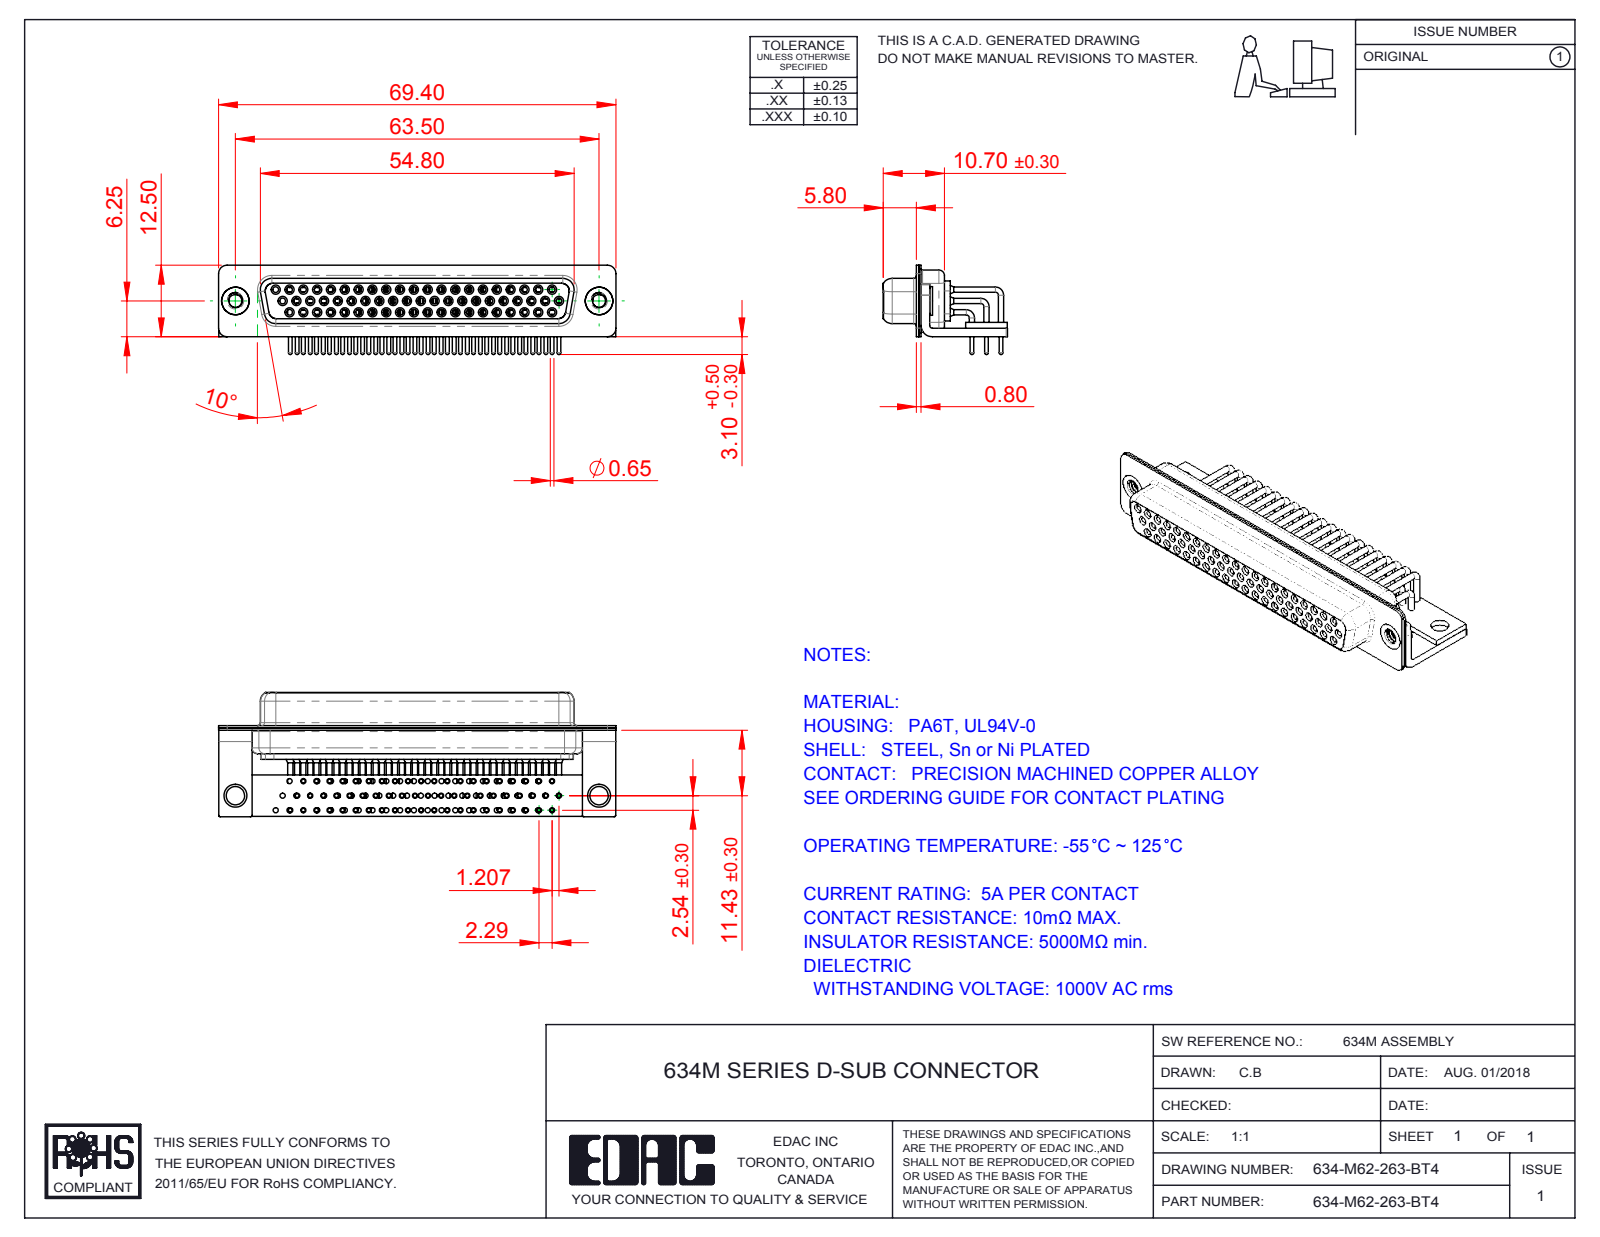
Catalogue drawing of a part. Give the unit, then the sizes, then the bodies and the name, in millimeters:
Units: millimetres
Overall size (bounding box): 69.4 × 21.7 × 15.6
Round holes (diameter × count): ⌀0.9 ×62, ⌀1 ×62, ⌀1.1 ×62, ⌀1.7 ×62, ⌀1.8 ×62, ⌀2 ×62, ⌀2.26 ×2, ⌀3.2 ×2, ⌀4 ×2, ⌀4.8 ×2
Round bosses / shafts (diameter × count): ⌀0.9 ×118, ⌀1.6 ×62, ⌀1.5 ×62, ⌀0.65 ×62, ⌀2 ×56, ⌀5 ×2, ⌀4.9 ×2
Partial cylindrical surfaces — rounded edges, fillets, slot ends (radius × count): R0.25 ×16, R1.5 ×16, R2 ×13, R1.35 ×8, R1.6 ×8, R0.5 ×5, R0.6 ×4, R0.65 ×4
Main face-to-face distances: 0.4, 2.3, 1.9, 1, 1.45, 8.95, 8.5, 0.85, 0.8, 9.35
Hole centre spacings: 7.24, 2.41, 9.65, 4.83, 14.48, 16.89, 2.81, 2.32
Volume: 6 132 mm³ · Surface area: 19 720 mm²
Bodies: 70 solids, 3739 faces (1023 planar, 1709 cylindrical, 1007 other)
Part name (STEP PRODUCT): 634-M62-263-BT4; 634M 4-40 Threaded Rivet_Stabilizer; 634M Stabilizer Bracket; 634M Housing_62 Contacts (+6 more)
STEP written by: SolidWorks 2016 (CONFIG_CONTROL_DESIGN)
